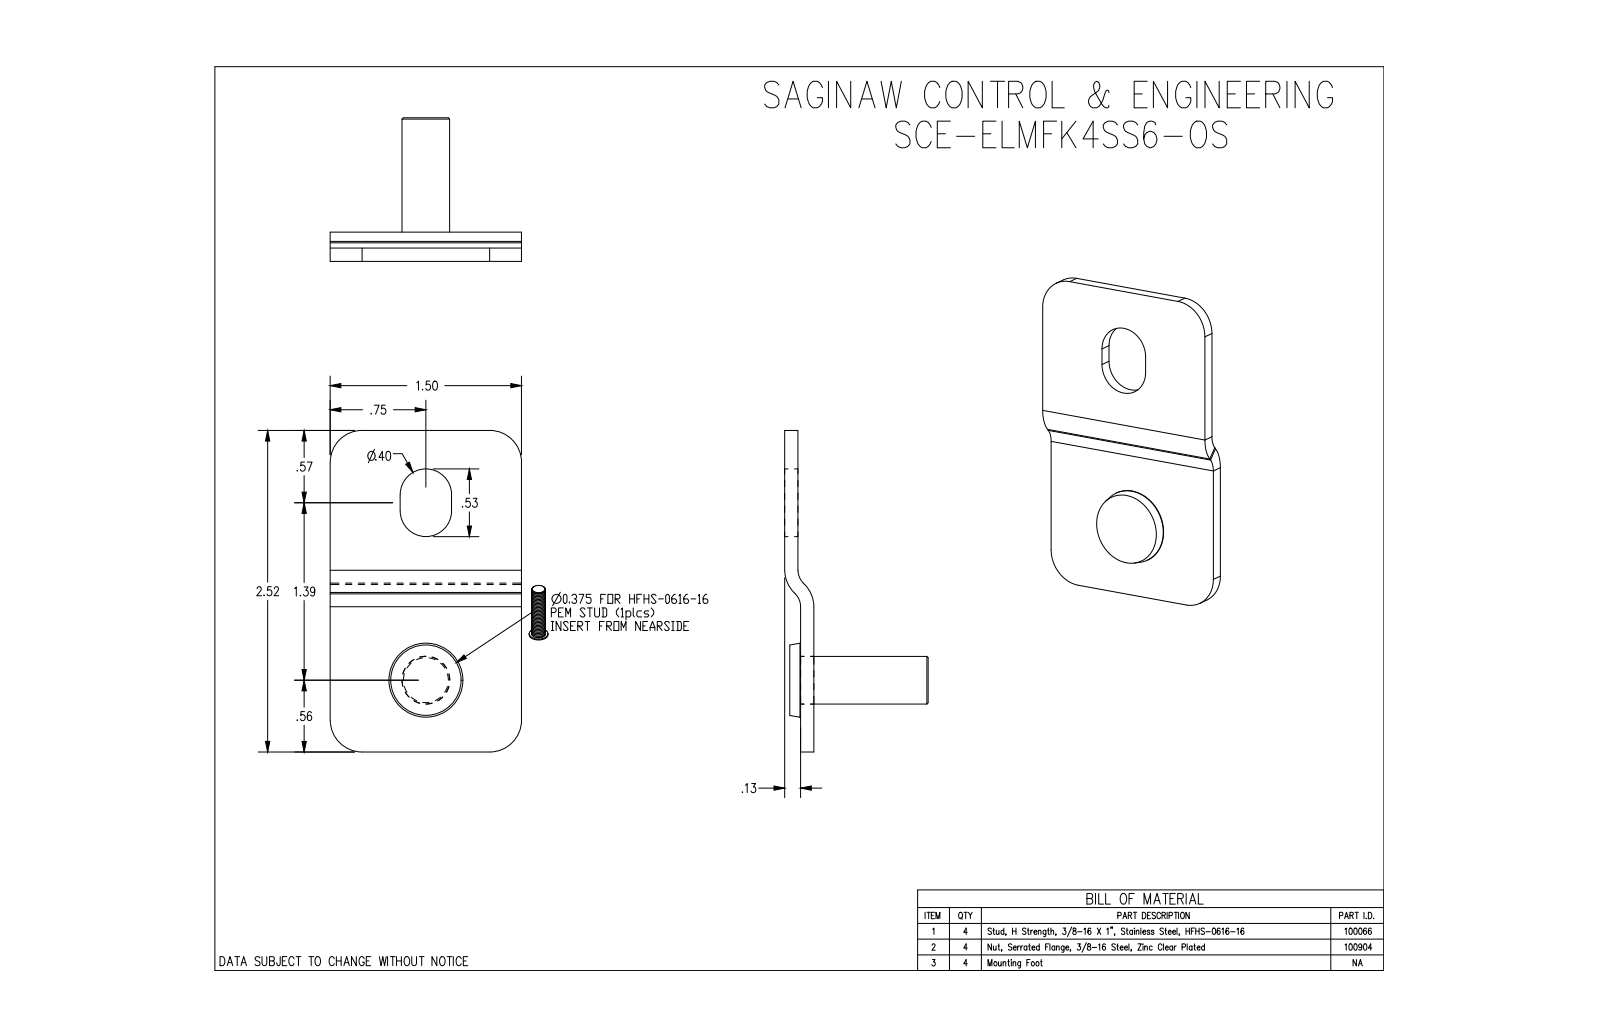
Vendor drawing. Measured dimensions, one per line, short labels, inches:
name: SCE-ELMFK4SS6-OS
written by: SolidWorks 2019 (AUTOMOTIVE_DESIGN)
unit: in
bodies: 12 solids, 296 faces (92 planar, 80 cylindrical, 124 other)
size: 22.415 × 20 × 1.125
volume: 2.24 in³; area: 45.78 in²
holes: 4× ⌀0.367, 2× ⌀0.375, 2× ⌀0.375
bosses: 4× ⌀0.58, 4× ⌀0.373
rounds: 24× R0.01, 16× R0.25, 8× R0.202, 4× R0.246, 2× R0.142, 2× R0.143
face distances: 0.104, 0.104, 0.125, 0.229, 0.021, 0.125, 18.5, 0.04, 0.064, 0.085
hole spacings: 18.5, 26.163
